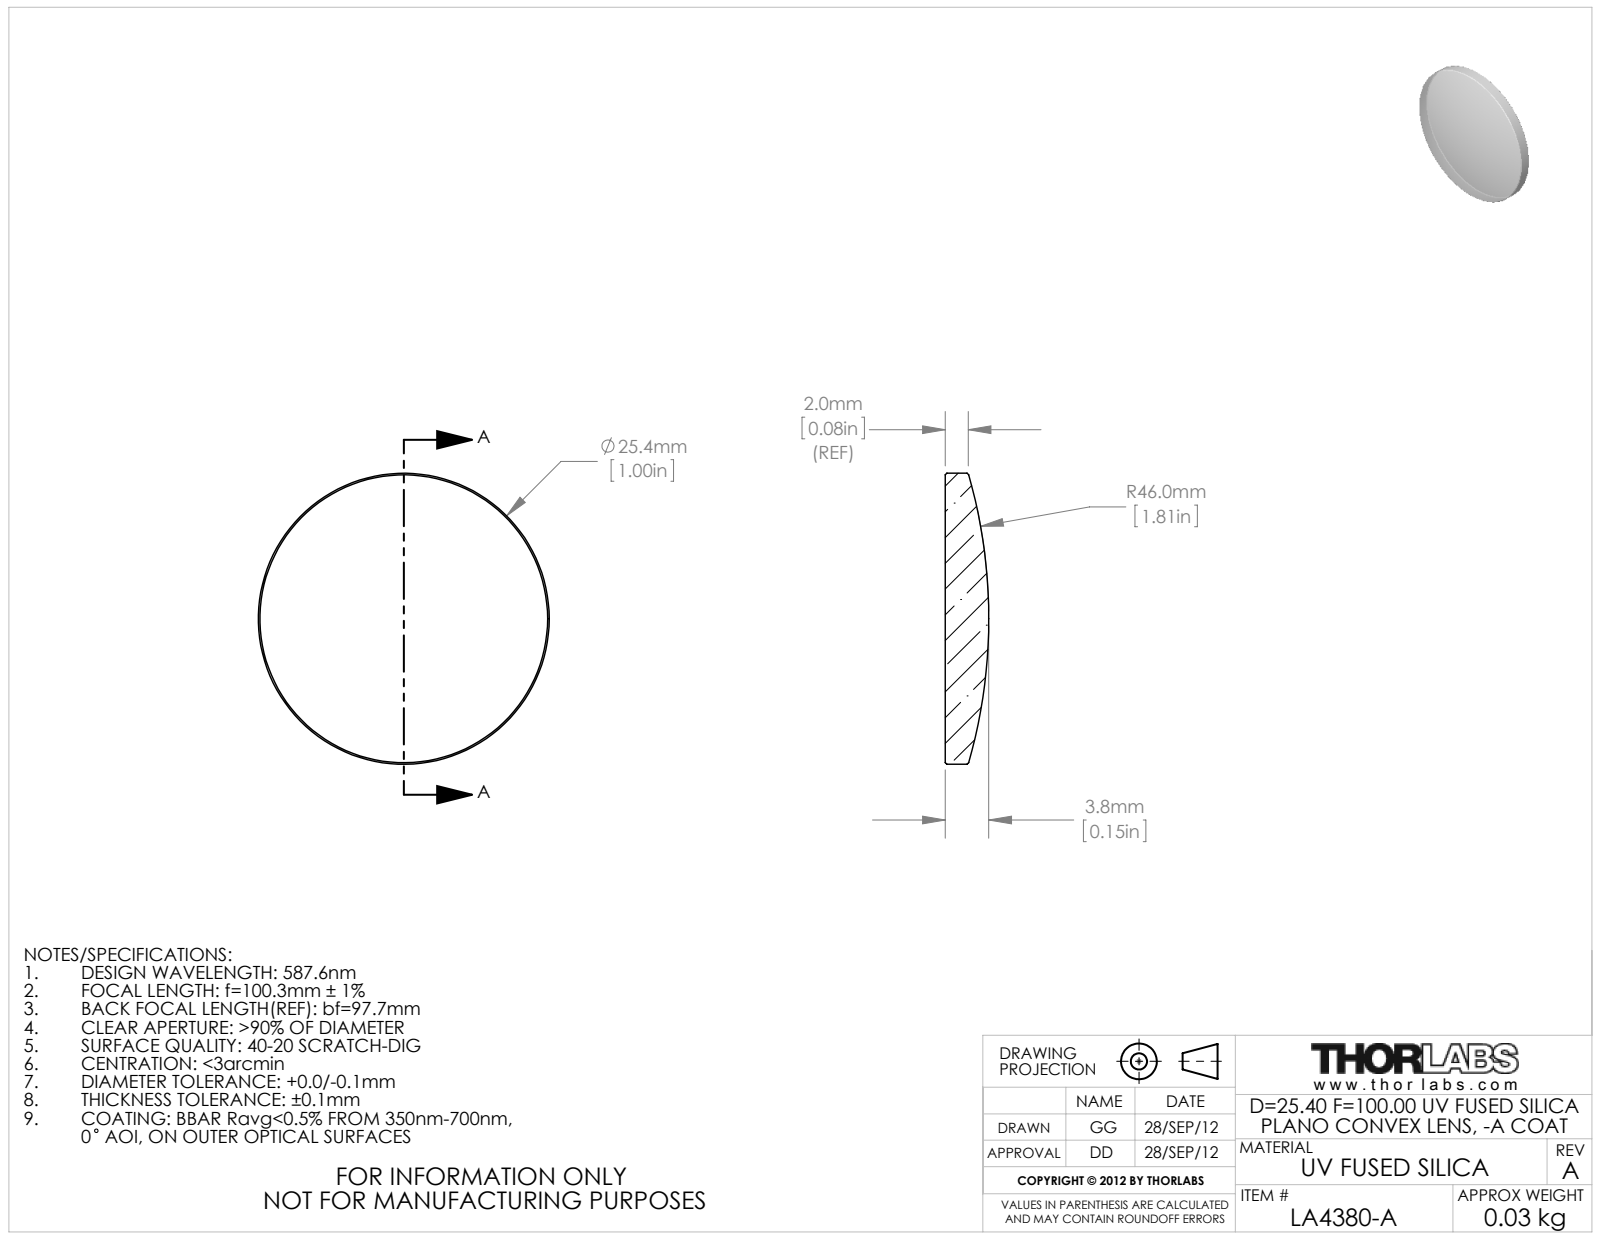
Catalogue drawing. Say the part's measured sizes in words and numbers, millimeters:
The part is named "24981-E0W". Its 3-D file was written by "SolidWorks 2011 (CONFIG_CONTROL_DESIGN)". It is 1 solid with 9 faces: 1 planar, 2 cylindrical and 6 other. Overall it measures 25.4 by 25.4 by 3.79 millimeters. Its volume is 1 468 cubic millimeters and its surface area 1 173 square millimeters. Round bosses or shafts: 1 of diameter 25.4.
